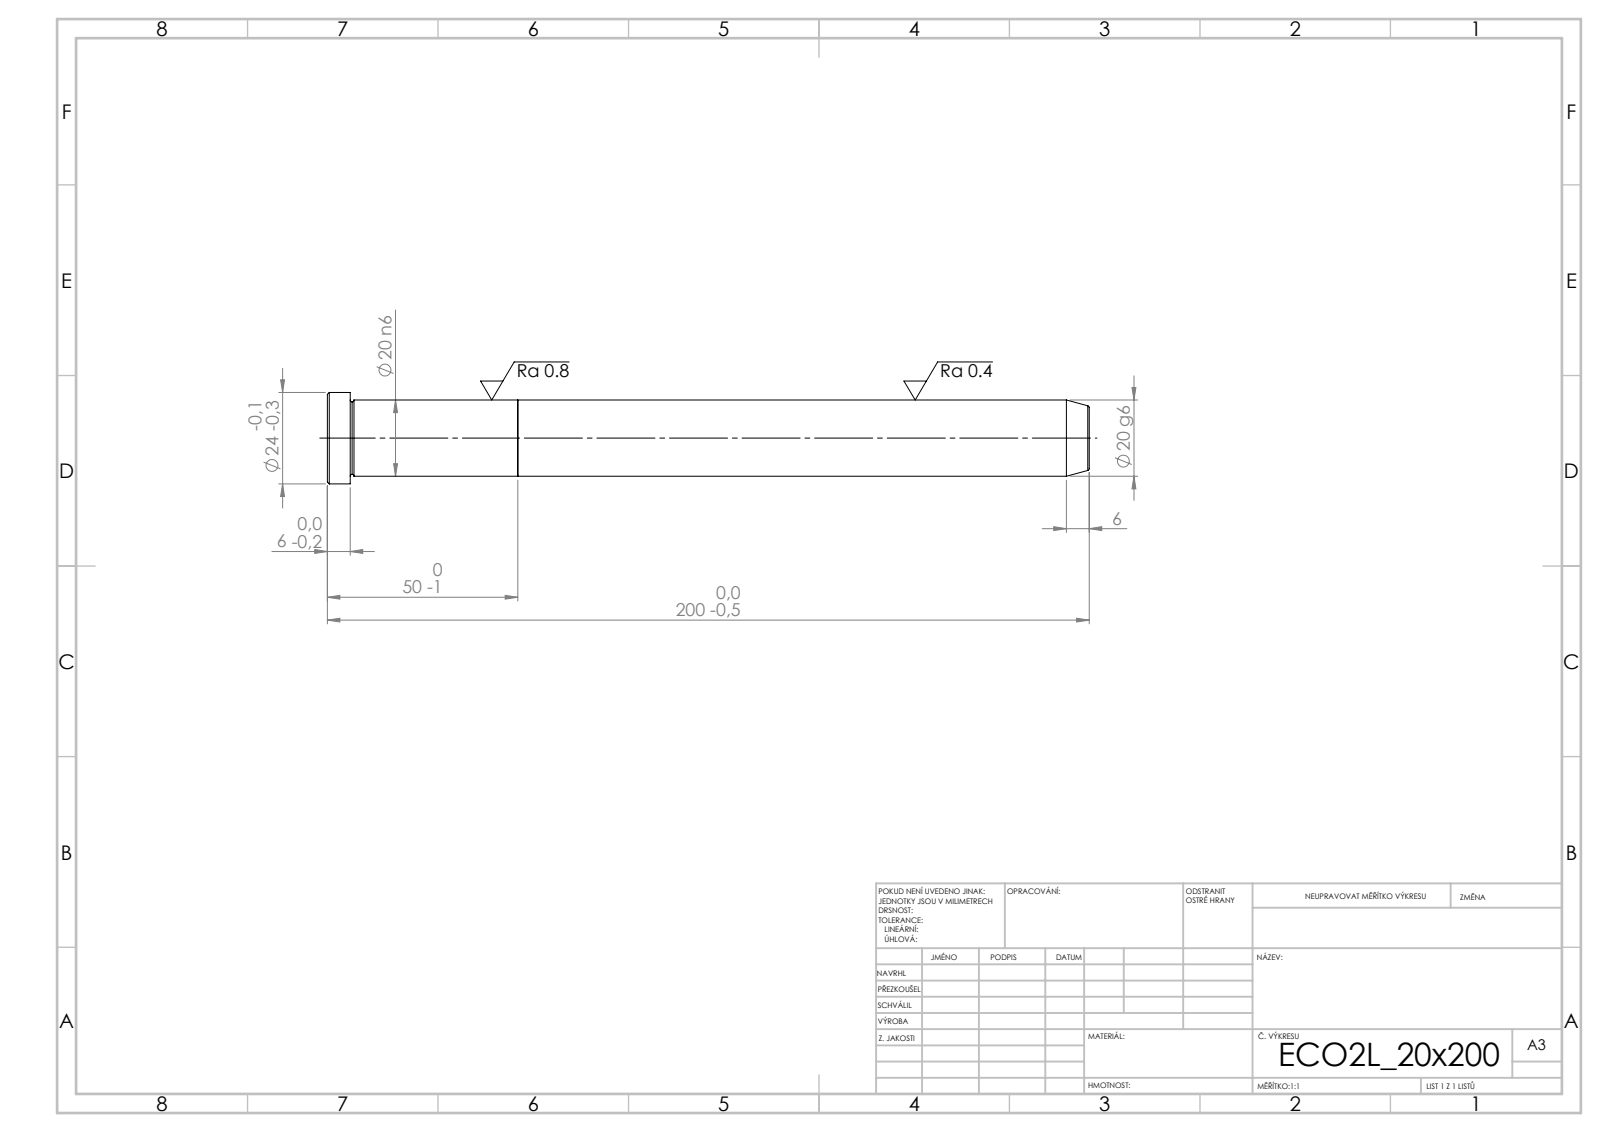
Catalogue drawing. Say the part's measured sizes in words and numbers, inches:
Its 3-D file was written by "SolidWorks 2019 (CONFIG_CONTROL_DESIGN)". It is 2 solids with 21 faces: 5 planar, 6 cylindrical and 10 other. Overall it measures 7.874 by 0.945 by 0.945 inches. Its volume is 3.865 cubic inches and its surface area 21.81 square inches. Round bosses or shafts: 1 of diameter 0.945, 1 of diameter 0.787. The main face-to-face distances are 1.969, 5.906, 7.874, 7.638, 1.732, 0.236.
